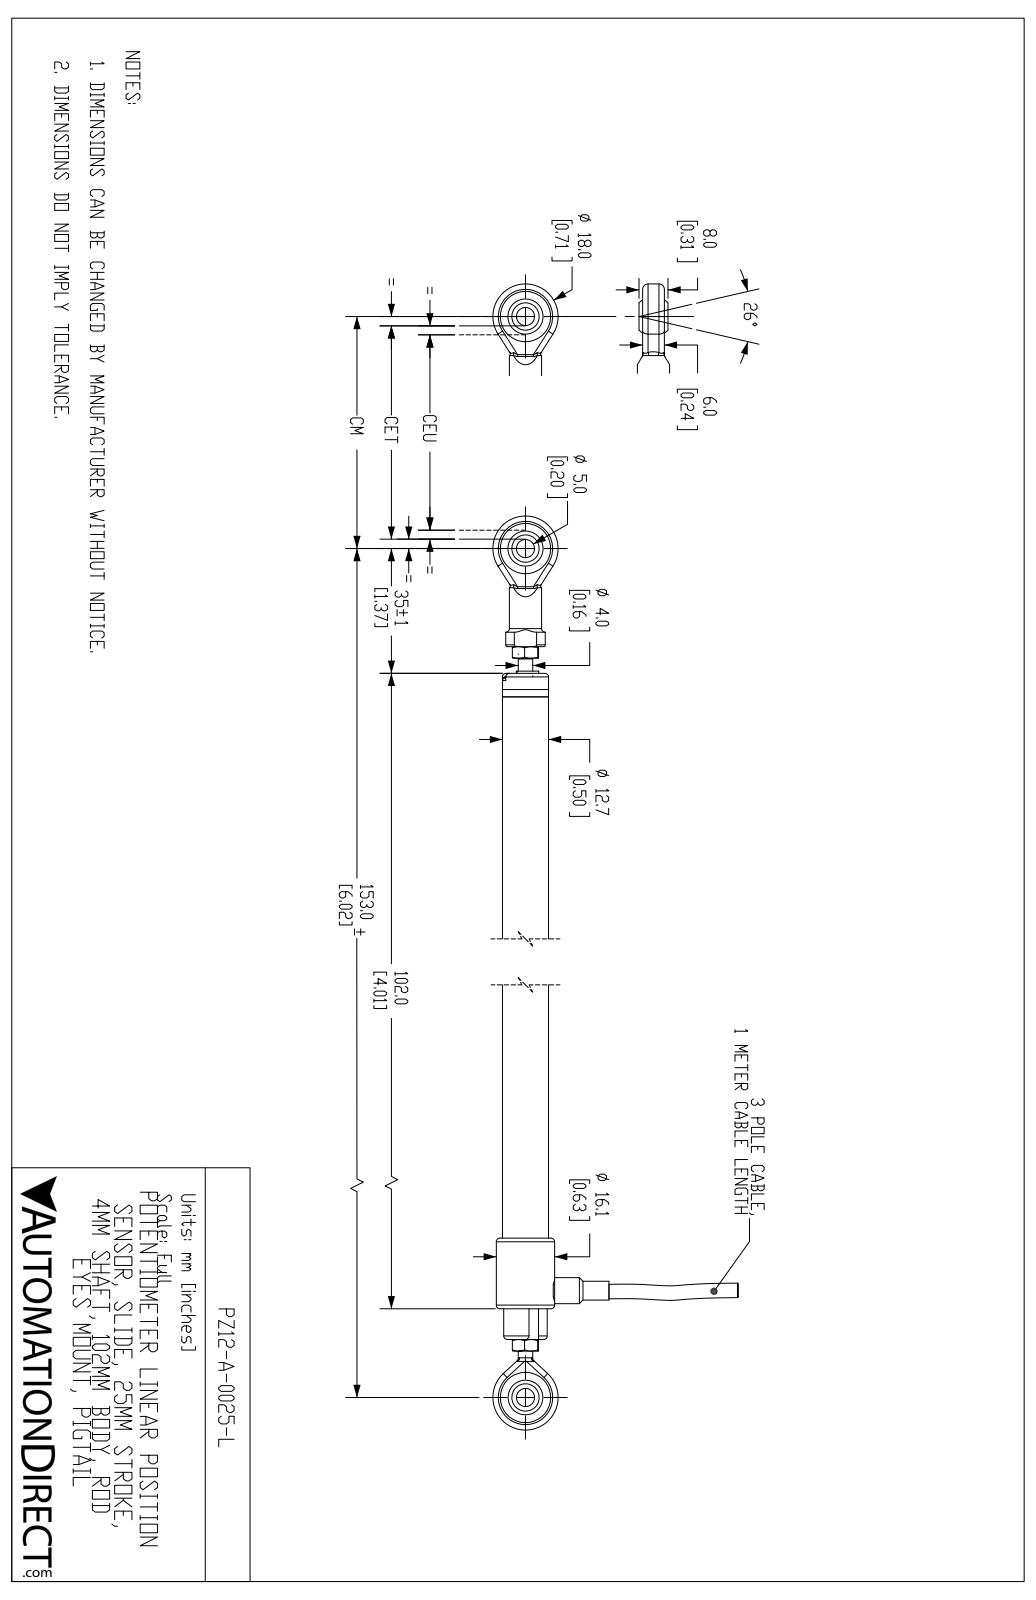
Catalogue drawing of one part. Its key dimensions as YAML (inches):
part_name: "PZ12-A-0025-L"
step_written_by: "SolidWorks 2019 (AUTOMOTIVE_DESIGN)"
units: inches
bodies: {solids: 18, faces: 648, planar: 168, cylindrical: 170, other: 310}
overall_size: [6.711, 2.671, 0.634]
volume: 1.304
surface_area: 21.21
round_holes:
  - {diameter: 0.138, count: 3}
  - {diameter: 0.039, count: 2}
  - {diameter: 0.055, count: 2}
  - {diameter: 0.079, count: 2}
  - {diameter: 0.197, count: 2}
  - {diameter: 0.547, count: 2}
  - {diameter: 0.126, count: 1}
  - {diameter: 0.13, count: 1}
  - {diameter: 0.201, count: 1}
  - {diameter: 0.508, count: 1}
round_bosses_or_shafts:
  - {diameter: 0.126, count: 4}
  - {diameter: 0.063, count: 4}
  - {diameter: 0.634, count: 1}
  - {diameter: 0.5, count: 1}
  - {diameter: 0.472, count: 1}
  - {diameter: 0.35, count: 1}
  - {diameter: 0.283, count: 1}
  - {diameter: 0.236, count: 1}
partial_cylinders:
  - {radius: 0.059, count: 8}
  - {radius: 0.01, count: 4}
  - {radius: 0.02, count: 2}
  - {radius: 0.039, count: 2}
  - {radius: 0.069, count: 2}
  - {radius: 0.354, count: 2}
  - {radius: 0.017, count: 1}
  - {radius: 0.103, count: 1}
face_to_face_distances: [0.079, 3.051, 3.13, 0.276, 0.224, 0.213, 0.236, 0.177, 4.305, 0.039]
hole_center_spacings: [0.189, 0.096, 0.167, 0.189, 0.248, 0.285, 0.339, 0.365]
